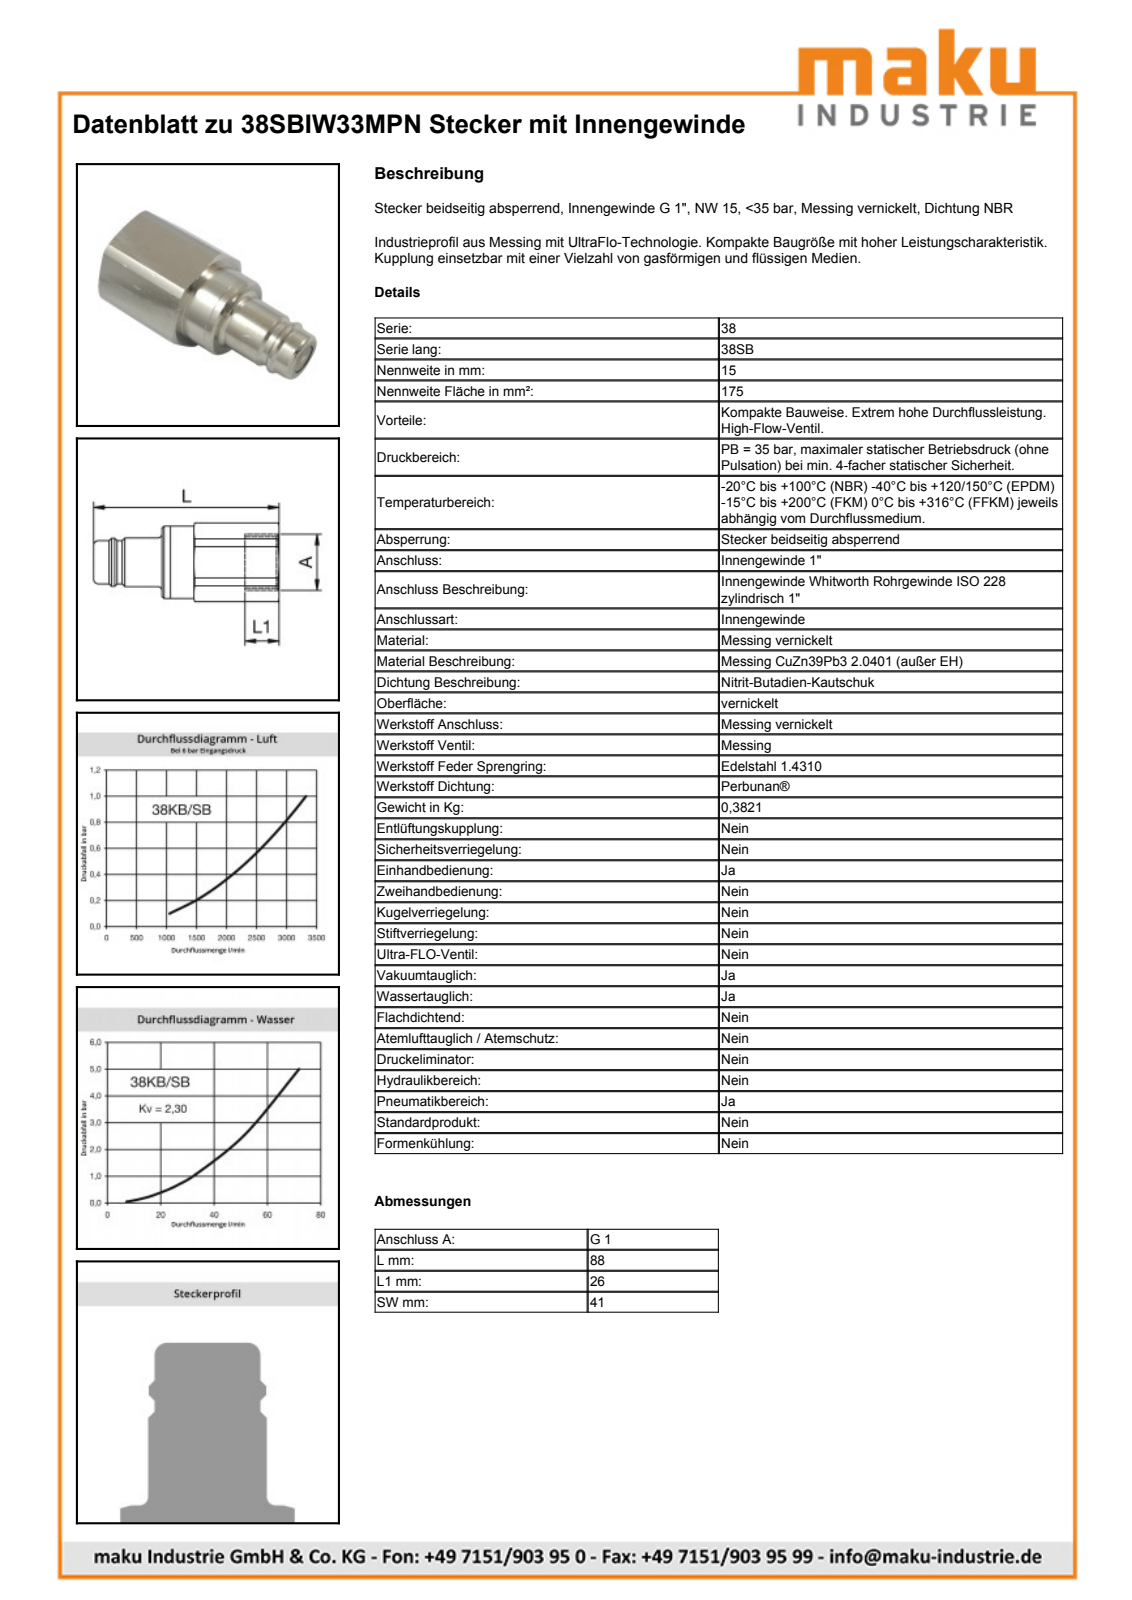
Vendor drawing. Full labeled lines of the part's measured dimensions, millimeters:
Part name (STEP PRODUCT): D107545
STEP written by: Autodesk Inventor 2013 (AUTOMOTIVE_DESIGN)
Units: millimetres
Bodies: 1 solid, 42 faces (11 planar, 12 cylindrical, 19 other)
Overall size (bounding box): 87.8 × 45 × 41.49
Volume: 62 507 mm³ · Surface area: 14 624 mm²
Round holes (diameter × count): ⌀33.25 ×1
Round bosses / shafts (diameter × count): ⌀34 ×1, ⌀22.85 ×1, ⌀22.6 ×1, ⌀20.3 ×1
Partial cylindrical surfaces — rounded edges, fillets, slot ends (radius × count): R22.5 ×1
Main face-to-face distances: 40.98, 41.02, 15.85, 41, 25.15, 14.7, 30.55, 55.7, 32.1, 46.8
